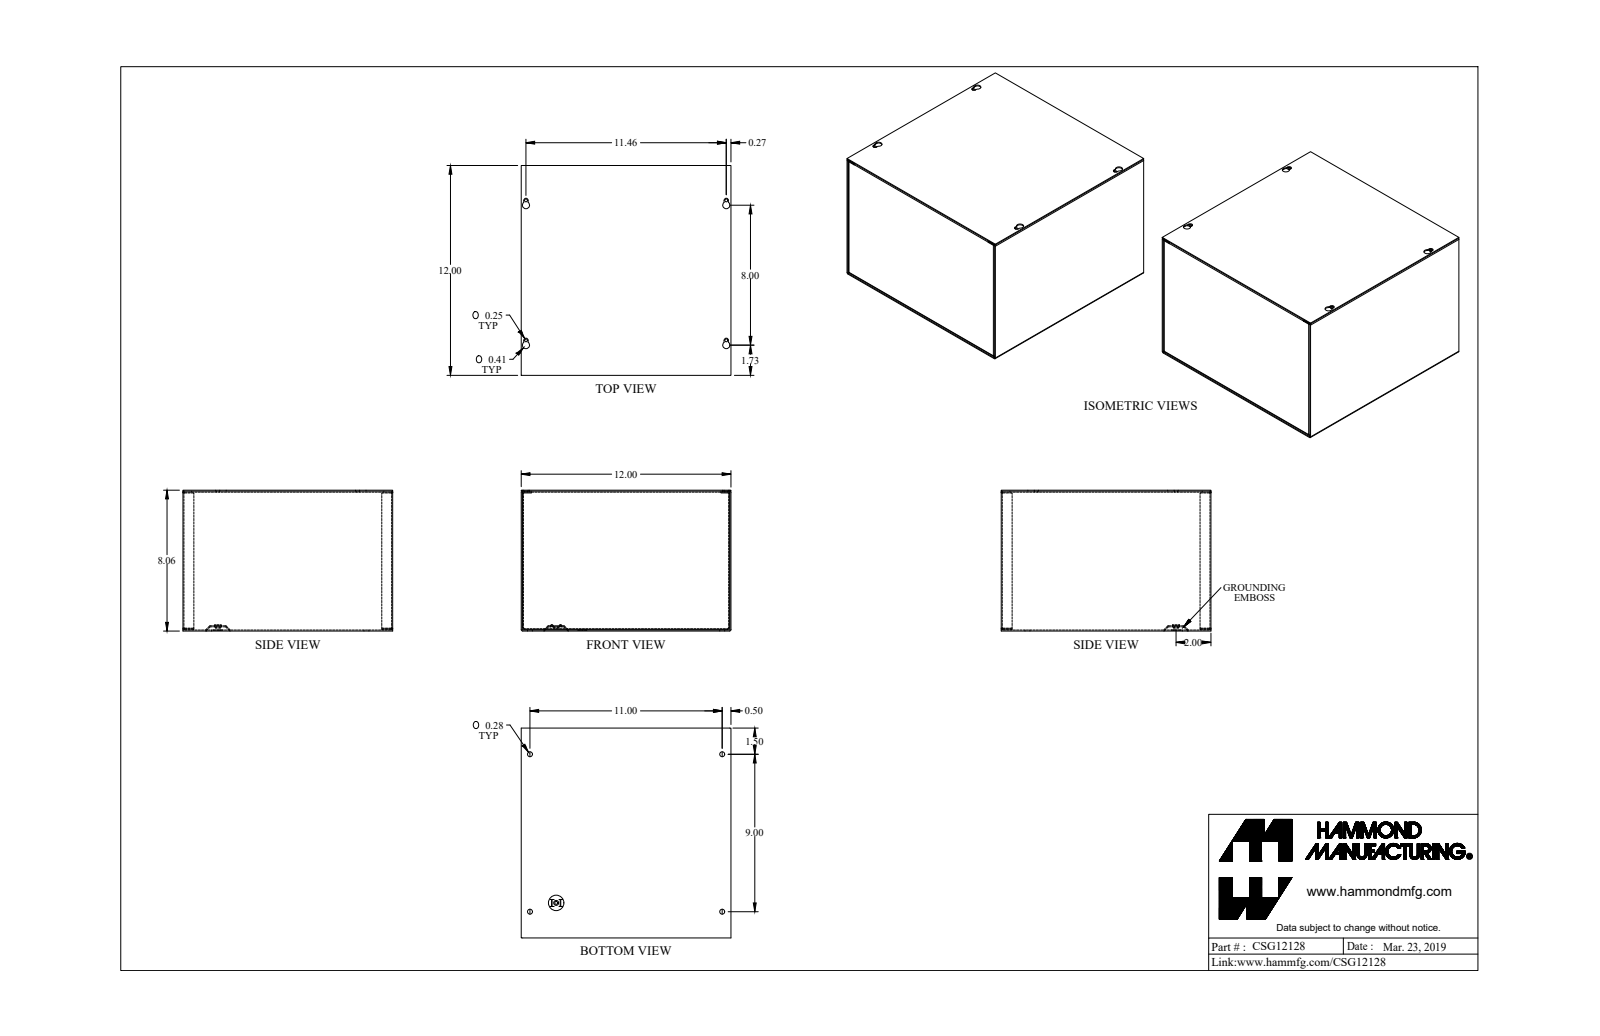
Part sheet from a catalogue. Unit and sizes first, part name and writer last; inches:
Units: inches
Overall size (bounding box): 12 × 12 × 8.057
Round holes (diameter × count): ⌀0.17 ×5, ⌀0.281 ×4, ⌀0.5 ×1
Round bosses / shafts (diameter × count): ⌀0.492 ×1, ⌀0.284 ×1
Partial cylindrical surfaces — rounded edges, fillets, slot ends (radius × count): R0.029 ×12, R0.086 ×12, R0.057 ×8, R0.125 ×4, R0.203 ×4
Main face-to-face distances: 0.057, 11.943, 8, 12, 11.886, 7.943, 8.057, 0.07, 11.873, 0.08
Hole centre spacings: 0.55, 8.503, 11.241, 14.084, 8, 9, 11, 11.46
Volume: 40.68 in³ · Surface area: 1 441 in²
Bodies: 4 solids, 205 faces (125 planar, 72 cylindrical, 8 other)
Part name (STEP PRODUCT): CSG12128_Default
STEP written by: SolidWorks 2019 (CONFIG_CONTROL_DESIGN)
